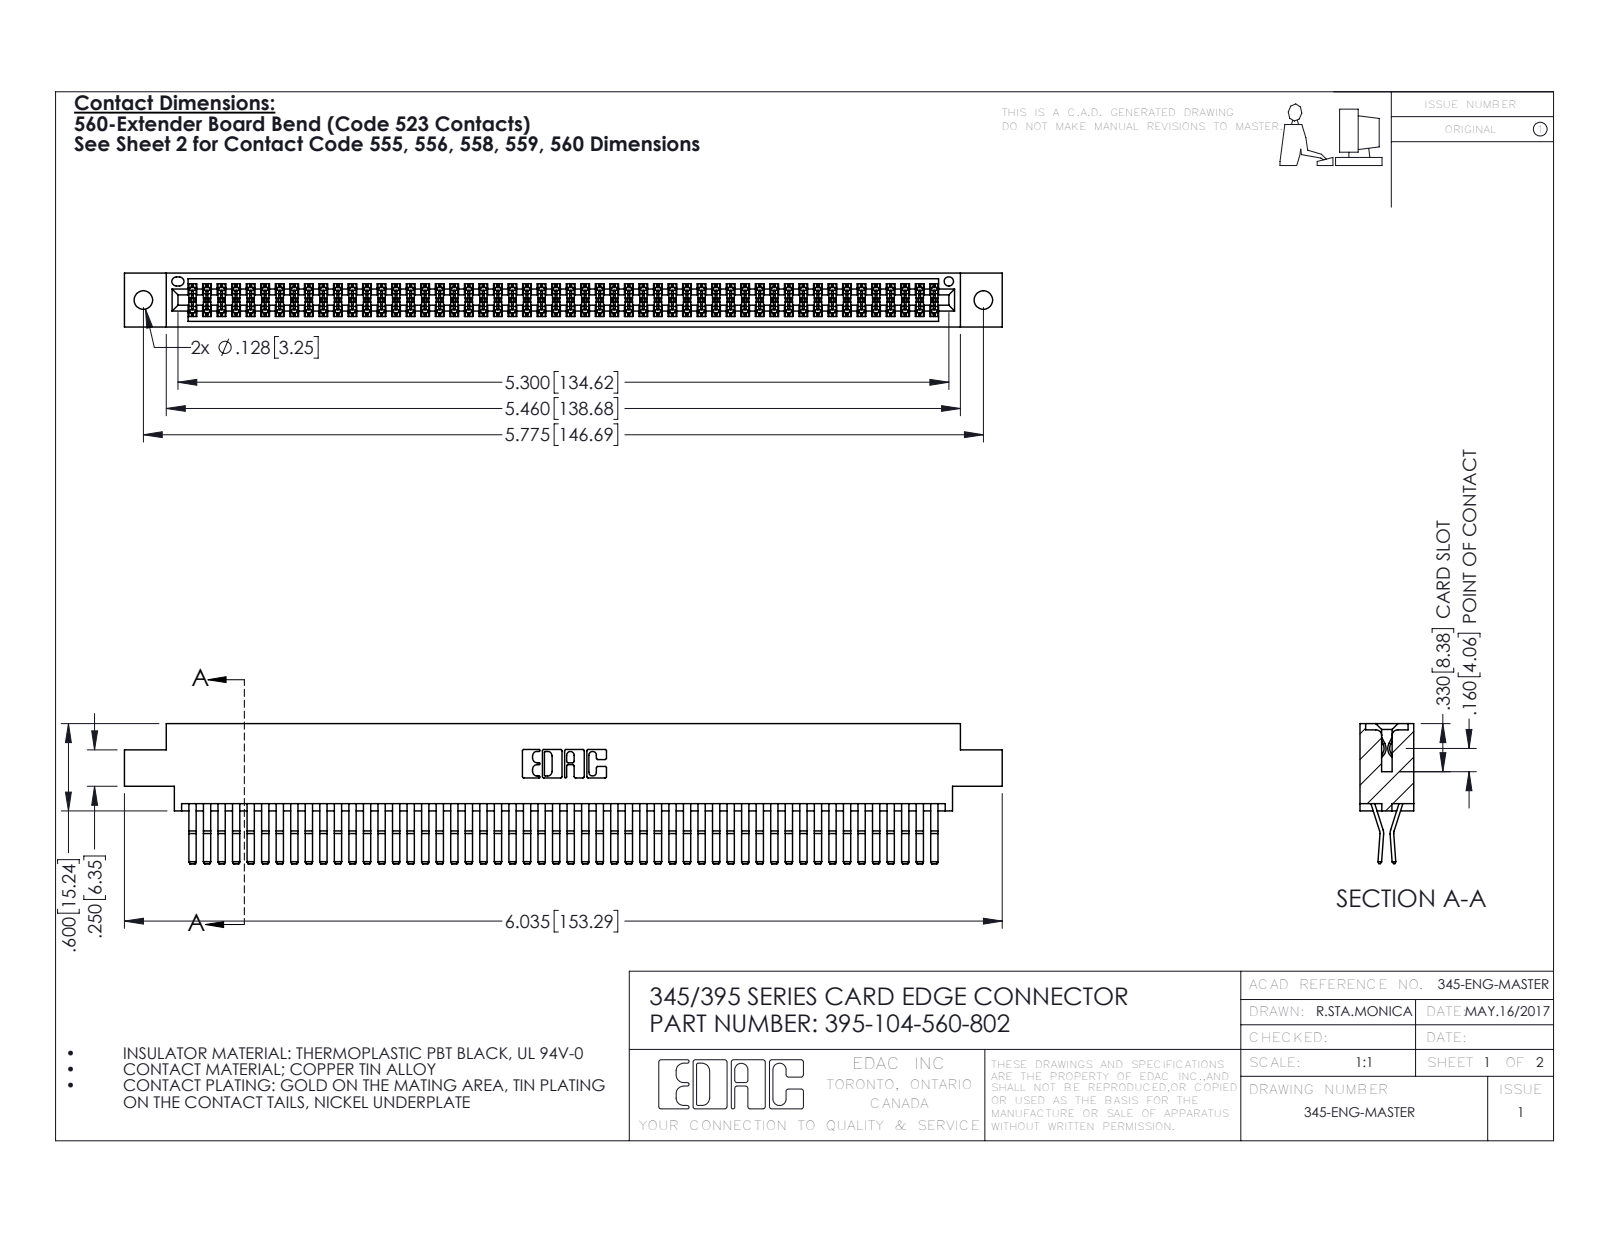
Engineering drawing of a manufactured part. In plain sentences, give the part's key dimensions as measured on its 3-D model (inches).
The part is named "345 Part_0.170 Offset - 0.128 Dia; 395-104-560-802; 345-292-001_560 Tail". Its 3-D file was written by "SolidWorks 2016 (CONFIG_CONTROL_DESIGN)". It is 105 solids with 5538 faces: 3516 planar, 2022 cylindrical and 0 other. Overall it measures 6.035 by 0.962 by 0.37 inches. Its volume is 0.947 cubic inches and its surface area 38.36 square inches. Round holes: 2 of diameter 0.128, 1 of diameter 0.064. Partial cylindrical surfaces (rounded edges, fillets, slot ends): 157 of radius 0.006, 22 of radius 0.01, 6 of radius 0.007, 6 of radius 0.031, 3 of radius 0.026, 2 of radius 0.01, 2 of radius 0.014, 2 of radius 0.019. The main face-to-face distances are 0.025, 0.298, 0.072, 0.37, 0.2, 0.098, 0.272, 0.225, 0.175, 0.149. The hole center spacings are 0.27, 5.539, 5.775.
